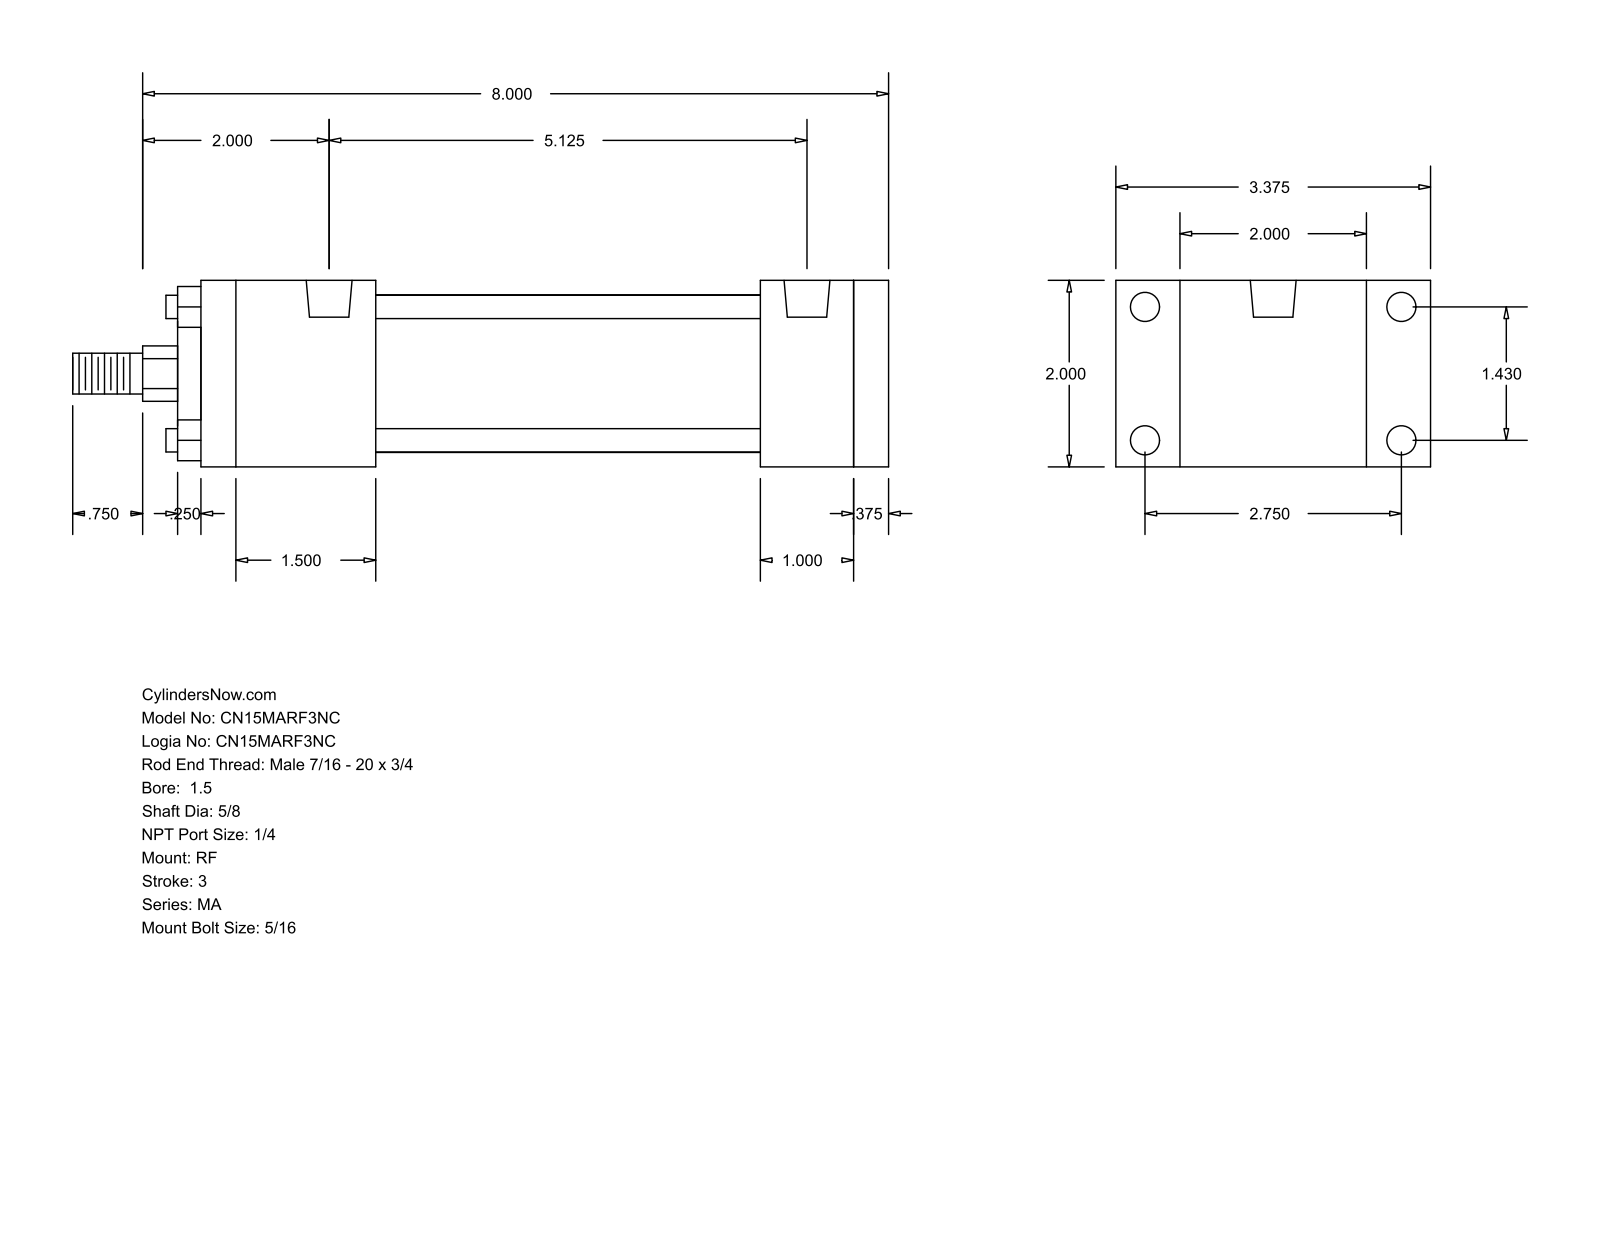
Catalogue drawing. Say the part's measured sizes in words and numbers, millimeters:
The part is named "MA_RF__0150_0.625". Its 3-D file was written by "GSSL Pune (CONFIG_CONTROL_DESIGN)". It is 0 solids with 92 faces: 64 planar, 28 cylindrical and 0 other. Overall it measures 222.25 by 85.72 by 50.8 millimeters. Round holes: 8 of diameter 7.94, 2 of diameter 12.49. Round bosses or shafts: 4 of diameter 6.35, 1 of diameter 42.93, 1 of diameter 28.57, 1 of diameter 15.88, 1 of diameter 11.11. Partial cylindrical surfaces (rounded edges, fillets, slot ends): 1 of radius 7.54. The main face-to-face distances are 50.8, 9.52, 177.8, 187.32, 25.4, 152.4, 34.92, 47.62, 104.78, 130.18. The hole center spacings are 36.32, 69.84, 78.72, 130.17.
